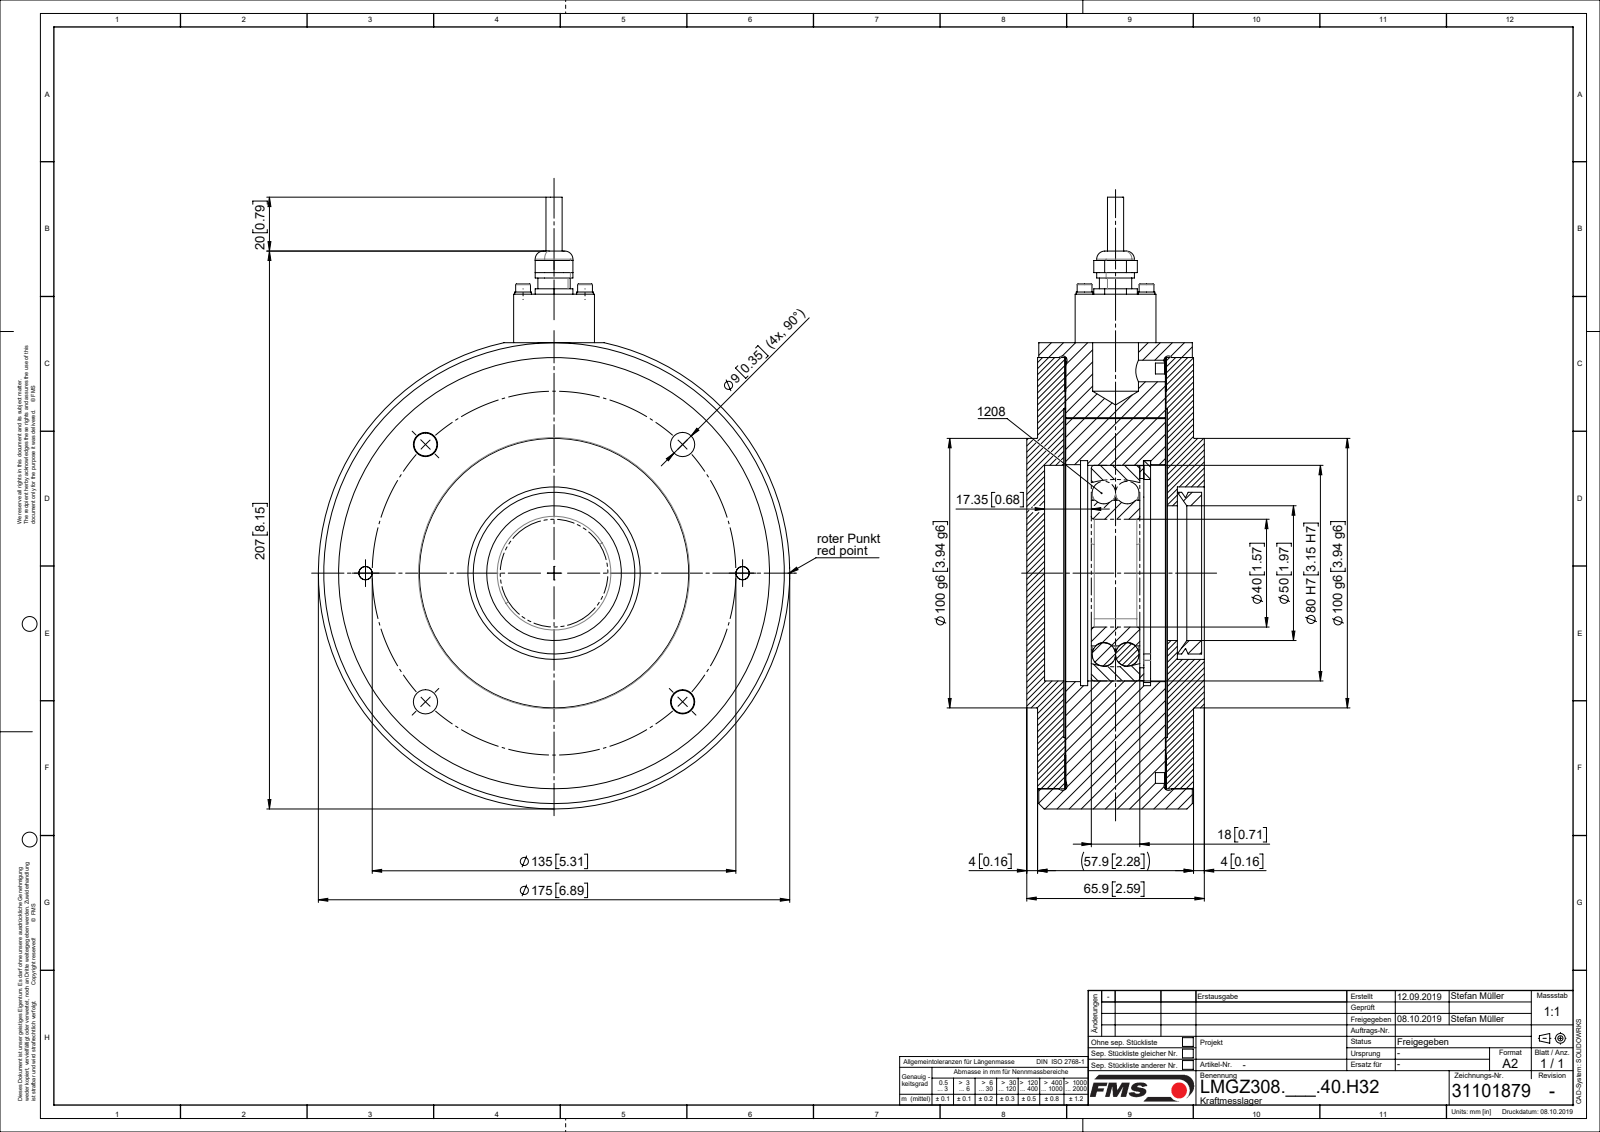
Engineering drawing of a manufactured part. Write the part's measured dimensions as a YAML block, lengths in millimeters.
part_name: "ZEICHNUNG2; L50049; L4857104; ~TEIL1 (+8 more)"
step_written_by: "Mechanical Desktop 2009 (CONFIG_CONTROL_DESIGN)"
units: millimeters
bodies: {solids: 22, faces: 360, planar: 105, cylindrical: 203, other: 52}
overall_size: [207, 175, 65.9]
volume: 1247000
surface_area: 268140
round_holes:
  - {diameter: 2.6, count: 4}
  - {diameter: 3.2, count: 4}
  - {diameter: 3.4, count: 4}
  - {diameter: 9, count: 4}
  - {diameter: 5.15, count: 2}
  - {diameter: 6.6, count: 2}
  - {diameter: 8.68, count: 2}
  - {diameter: 11, count: 2}
  - {diameter: 6, count: 1}
  - {diameter: 11.28, count: 1}
  - {diameter: 23, count: 1}
  - {diameter: 40, count: 1}
round_bosses_or_shafts:
  - {diameter: 6.2, count: 4}
  - {diameter: 5.5, count: 4}
  - {diameter: 3, count: 4}
  - {diameter: 10, count: 2}
  - {diameter: 6, count: 2}
  - {diameter: 175, count: 1}
  - {diameter: 160, count: 1}
  - {diameter: 100, count: 1}
partial_cylinders:
  - {radius: 7.5, count: 2}
face_to_face_distances: [37.25, 10.2, 10.45, 47.45, 47.7, 37, 37.5, 4, 9.7, 48.2]
hole_center_spacings: [16.26, 23, 52.67, 67.5, 95.46, 127.04, 32.53, 70]
